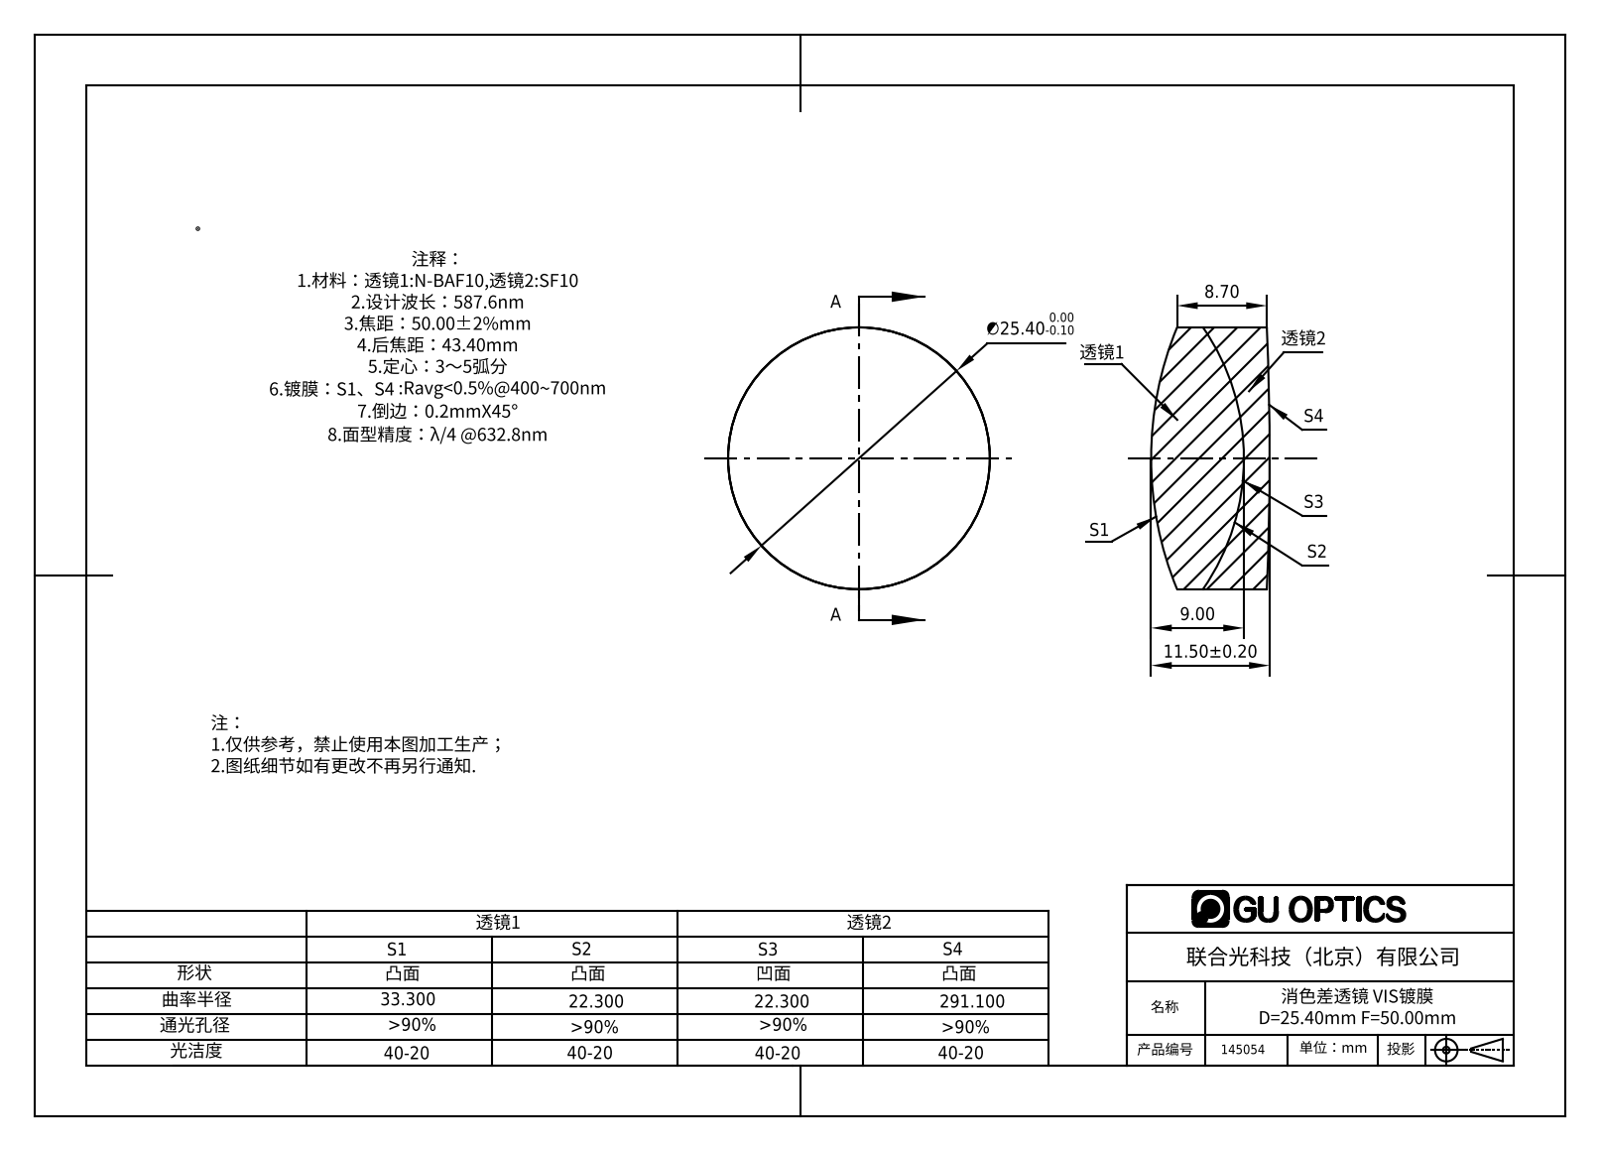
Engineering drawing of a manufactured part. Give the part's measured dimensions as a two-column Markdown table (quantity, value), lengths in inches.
| quantity | value |
| --- | --- |
| part name | 145054 |
| STEP written by | SolidWorks 2016 (AUTOMOTIVE_DESIGN) |
| units | inches |
| bodies | 2 solids, 12 faces (0 planar, 4 cylindrical, 8 other) |
| overall size | 1 × 1 × 0.453 |
| volume | 0.313 in³ |
| surface area | 4.404 in² |
| round bosses / shafts (diameter × count) | 1 × 1 |
